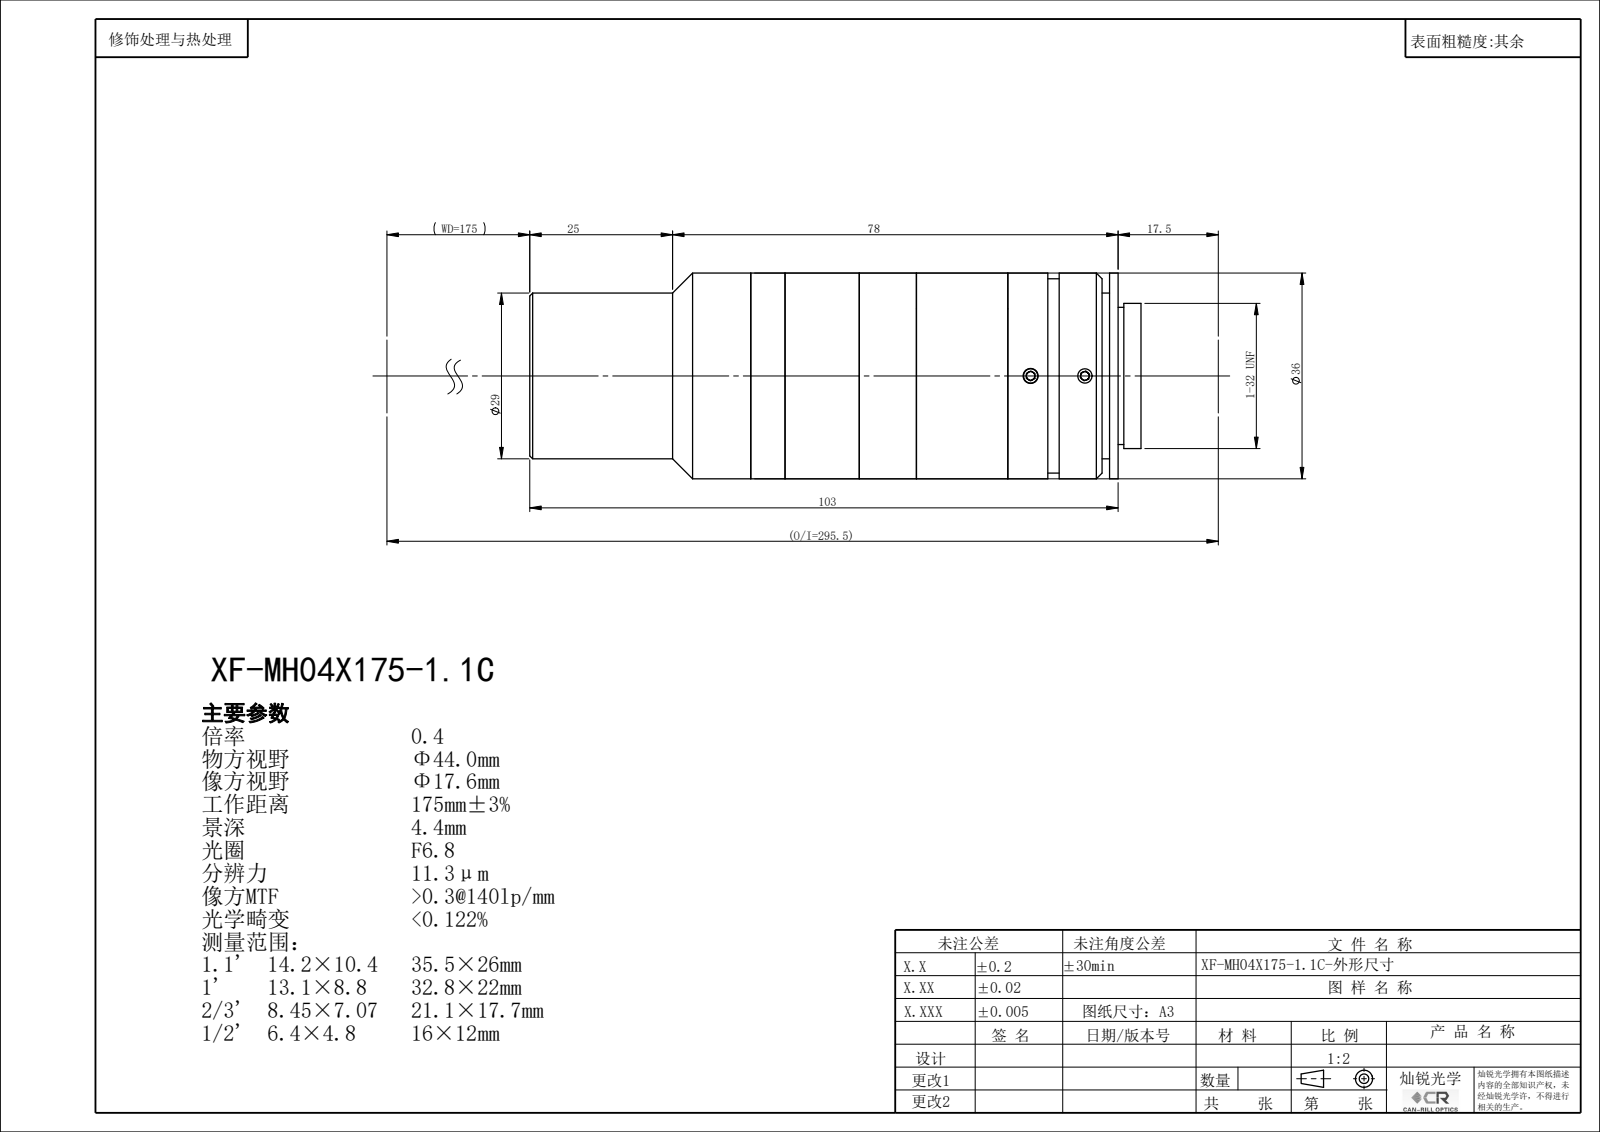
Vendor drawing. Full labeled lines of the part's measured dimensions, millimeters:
Part name (STEP PRODUCT): XF-MH04X175-1.1C
STEP written by: SolidWorks 2022 (CONFIG_CONTROL_DESIGN)
Units: millimetres
Bodies: 0 solids, 142 faces (70 planar, 44 cylindrical, 28 other)
Overall size (bounding box): 106.99 × 36 × 36
Round holes (diameter × count): ⌀2.5 ×3, ⌀20 ×1, ⌀22.4 ×1, ⌀24 ×1, ⌀24.9 ×1, ⌀26 ×1, ⌀26.4 ×1
Round bosses / shafts (diameter × count): ⌀36 ×1, ⌀34 ×1, ⌀29 ×1, ⌀25.4 ×1
Main face-to-face distances: 19.31, 1.5, 17.81, 33.81, 16, 35.31, 10, 26, 43.81, 45.31
